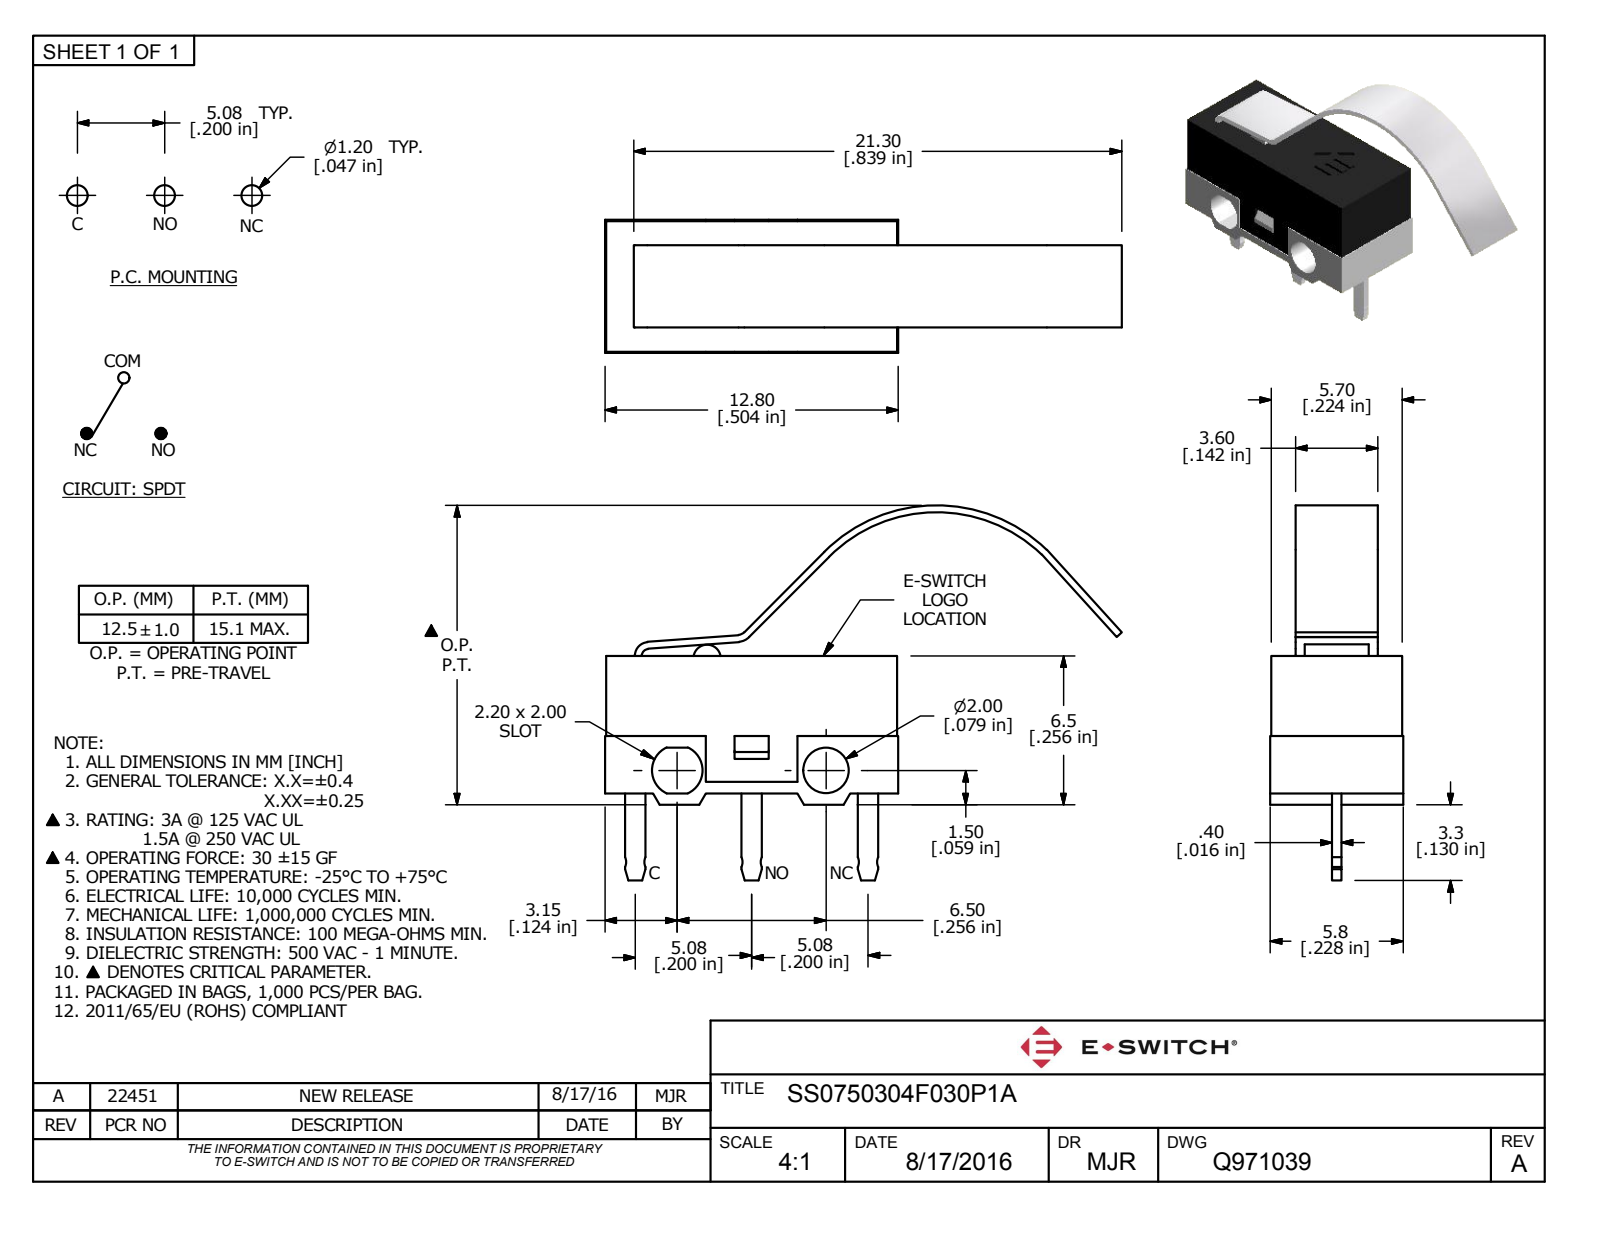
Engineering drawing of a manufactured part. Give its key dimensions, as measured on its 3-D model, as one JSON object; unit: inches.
{"part_name": "SS0750304F030P1A", "step_written_by": "Autodesk Inventor 2022 (AUTOMOTIVE_DESIGN)", "units": "inches", "bodies": {"solids": 1, "faces": 221, "planar": 174, "cylindrical": 31, "other": 16}, "overall_size": [0.882, 0.678, 0.228], "volume_in3": 0.017, "surface_area_in2": 1.42, "round_holes": [[0.079, 1]], "partial_cylinders_radius": [[0.02, 6], [0.005, 2], [0.024, 2], [0.012, 1], [0.015, 1], [0.027, 1], [0.043, 1], [0.261, 1]], "face_to_face_distances": [0.02, 0.022, 0.236, 0.118, 0.205, 0.138, 0.098, 0.217, 0.185, 0.224]}
